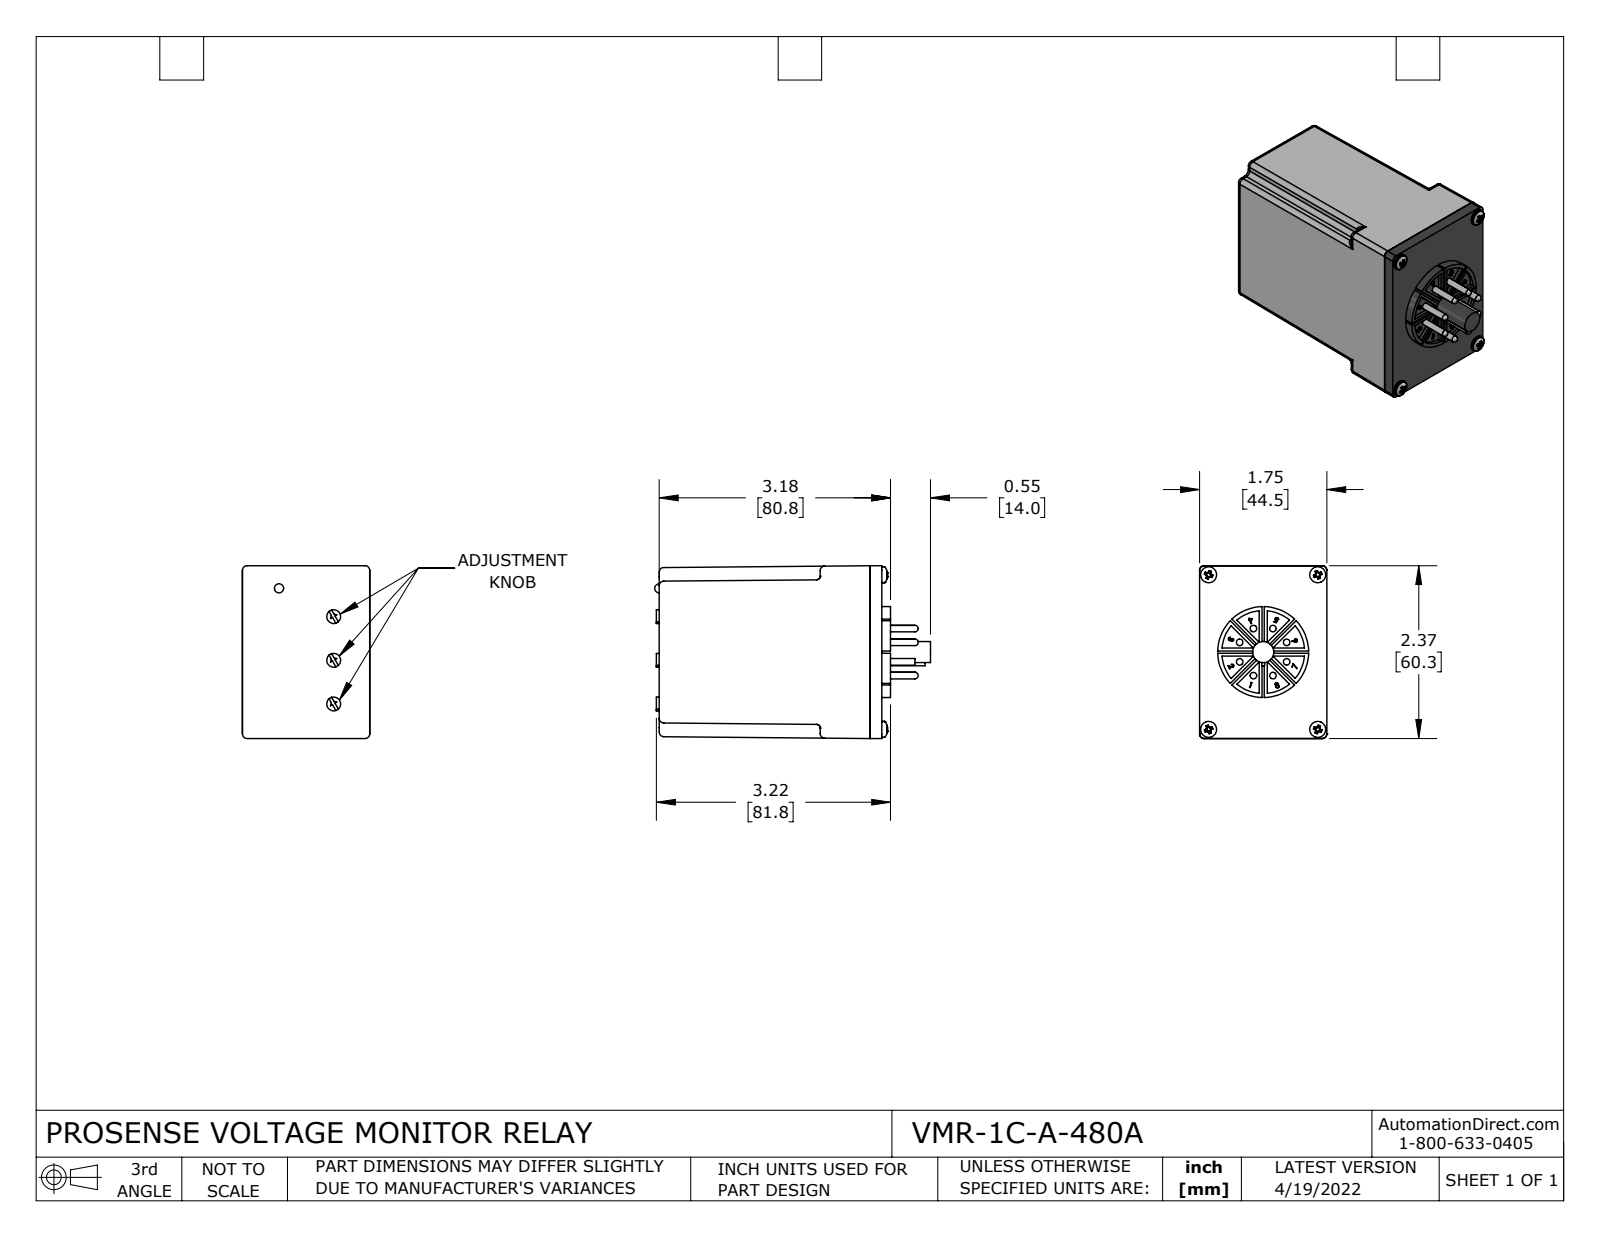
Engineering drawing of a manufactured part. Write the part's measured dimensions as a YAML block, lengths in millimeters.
part_name: "VMR-1C-A-480A"
step_written_by: "SolidWorks 2021 (CONFIG_CONTROL_DESIGN)"
units: millimeters
bodies: {solids: 18, faces: 574, planar: 249, cylindrical: 170, other: 155}
overall_size: [96.3, 60.3, 44.5]
volume: 200700
surface_area: 28850
round_holes:
  - {diameter: 3.2, count: 4}
round_bosses_or_shafts:
  - {diameter: 2.3, count: 8}
  - {diameter: 5.6, count: 4}
  - {diameter: 4.8, count: 3}
  - {diameter: 31.8, count: 1}
  - {diameter: 7.4, count: 1}
partial_cylinders:
  - {radius: 1.6, count: 32}
  - {radius: 0.1, count: 8}
  - {radius: 1.3, count: 4}
  - {radius: 14.5, count: 1}
face_to_face_distances: [73.7, 4.1, 77.7, 1.8, 5.8, 79.5, 4.8, 1.3, 3, 7.1]
hole_center_spacings: [38.1, 54, 66.1]
